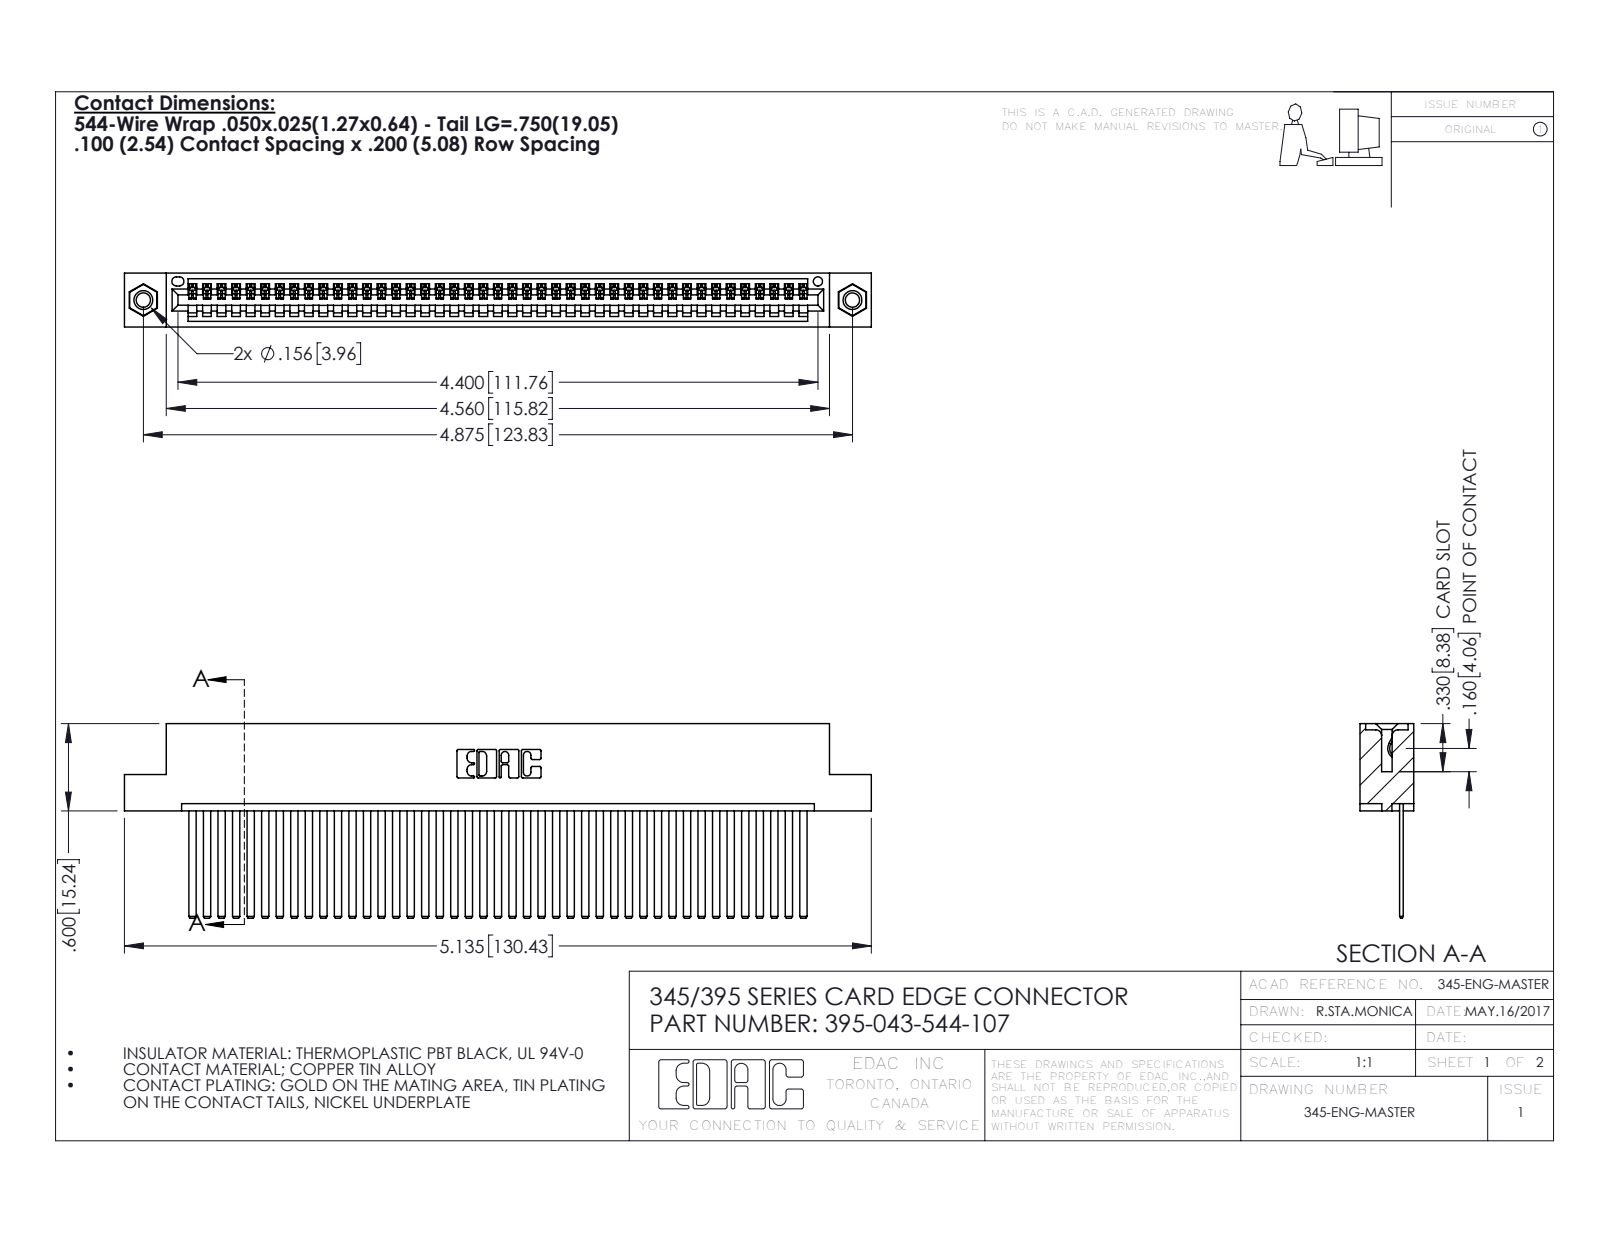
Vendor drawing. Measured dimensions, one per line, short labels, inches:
name: 345 Part_Flush Mounting Lugs - 0.156 Dia-TI; 395-043-544-107; 345-250-001_345-250-005-103; 345-292-001_345-293-144
written by: SolidWorks 2016 (CONFIG_CONTROL_DESIGN)
unit: in
bodies: 46 solids, 2422 faces (1660 planar, 746 cylindrical, 16 other)
size: 5.135 × 1.337 × 0.37
volume: 0.786 in³; area: 28.92 in²
holes: 2× ⌀0.098, 2× ⌀0.125, 2× ⌀0.156, 1× ⌀0.064
bosses: 2× ⌀0.155
rounds: 86× R0.006, 22× R0.01, 6× R0.007, 6× R0.031, 3× R0.026, 2× R0.031, 2× R0.04, 1× R0.014
face distances: 0.072, 0.298, 0.025, 0.098, 0.272, 0.37, 0.2, 0.225, 0.149, 0.072
hole spacings: 0.27, 4.639, 4.875
